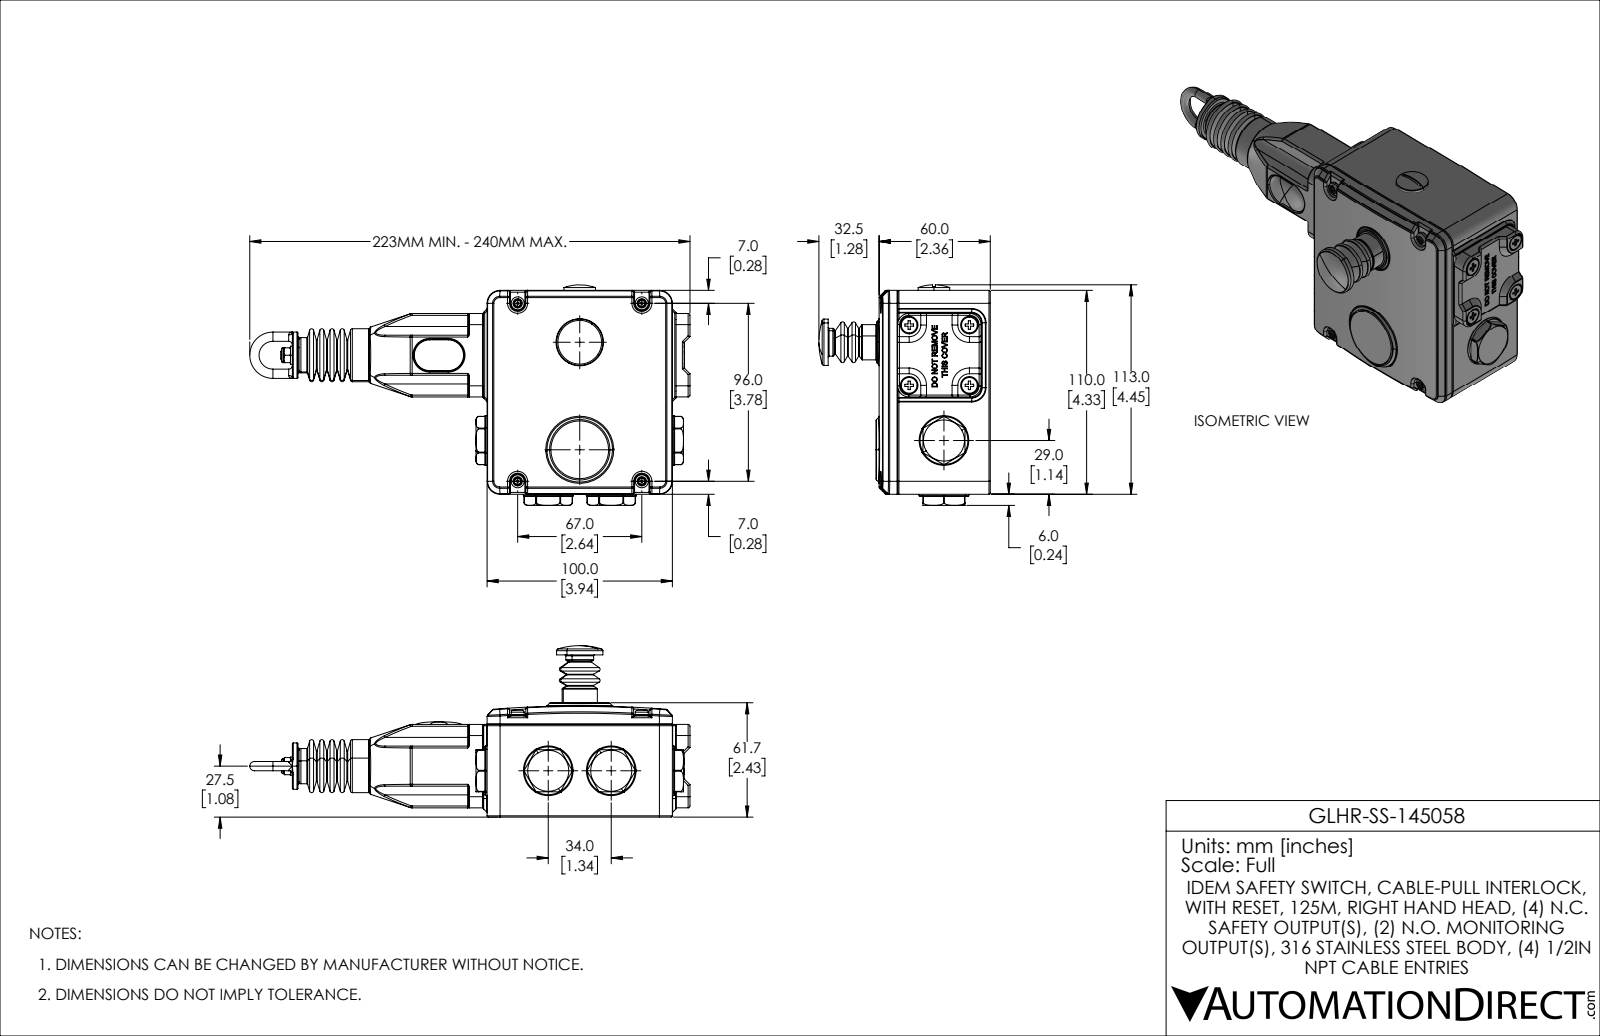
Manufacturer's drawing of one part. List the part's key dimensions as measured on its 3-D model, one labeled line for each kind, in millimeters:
Part name (STEP PRODUCT): GLHR-SS-145058
STEP written by: SolidWorks 2021 (AUTOMOTIVE_DESIGN)
Units: millimetres
Bodies: 34 solids, 3522 faces (955 planar, 1161 cylindrical, 1406 other)
Overall size (bounding box): 238.1 × 116.7 × 92.8
Volume: 288 700 mm³ · Surface area: 168 300 mm²
Round holes (diameter × count): ⌀5 ×9, ⌀5.3 ×9, ⌀9.6 ×8, ⌀9 ×5, ⌀3.3 ×4, ⌀4 ×4, ⌀4.1 ×4, ⌀4.8 ×4, ⌀5.4 ×4, ⌀5.8 ×4, ⌀3 ×3, ⌀4.4 ×3
Round bosses / shafts (diameter × count): ⌀5 ×11, ⌀8.5 ×8, ⌀4.4 ×8, ⌀7 ×5, ⌀3.5 ×4, ⌀1.3 ×4, ⌀24 ×3, ⌀23.8 ×3
Partial cylindrical surfaces — rounded edges, fillets, slot ends (radius × count): R0.5 ×206, R1 ×160, R0.2 ×64, R0.7 ×48, R0.2 ×14, R0.3 ×12, R0.1 ×8, R0.8 ×8
Main face-to-face distances: 1, 3.5, 55.4, 2, 2.9, 52.5, 102, 4, 110, 8.5
Hole centre spacings: 32.5, 32.5, 23, 9.5, 22.9, 23, 23, 32.5
